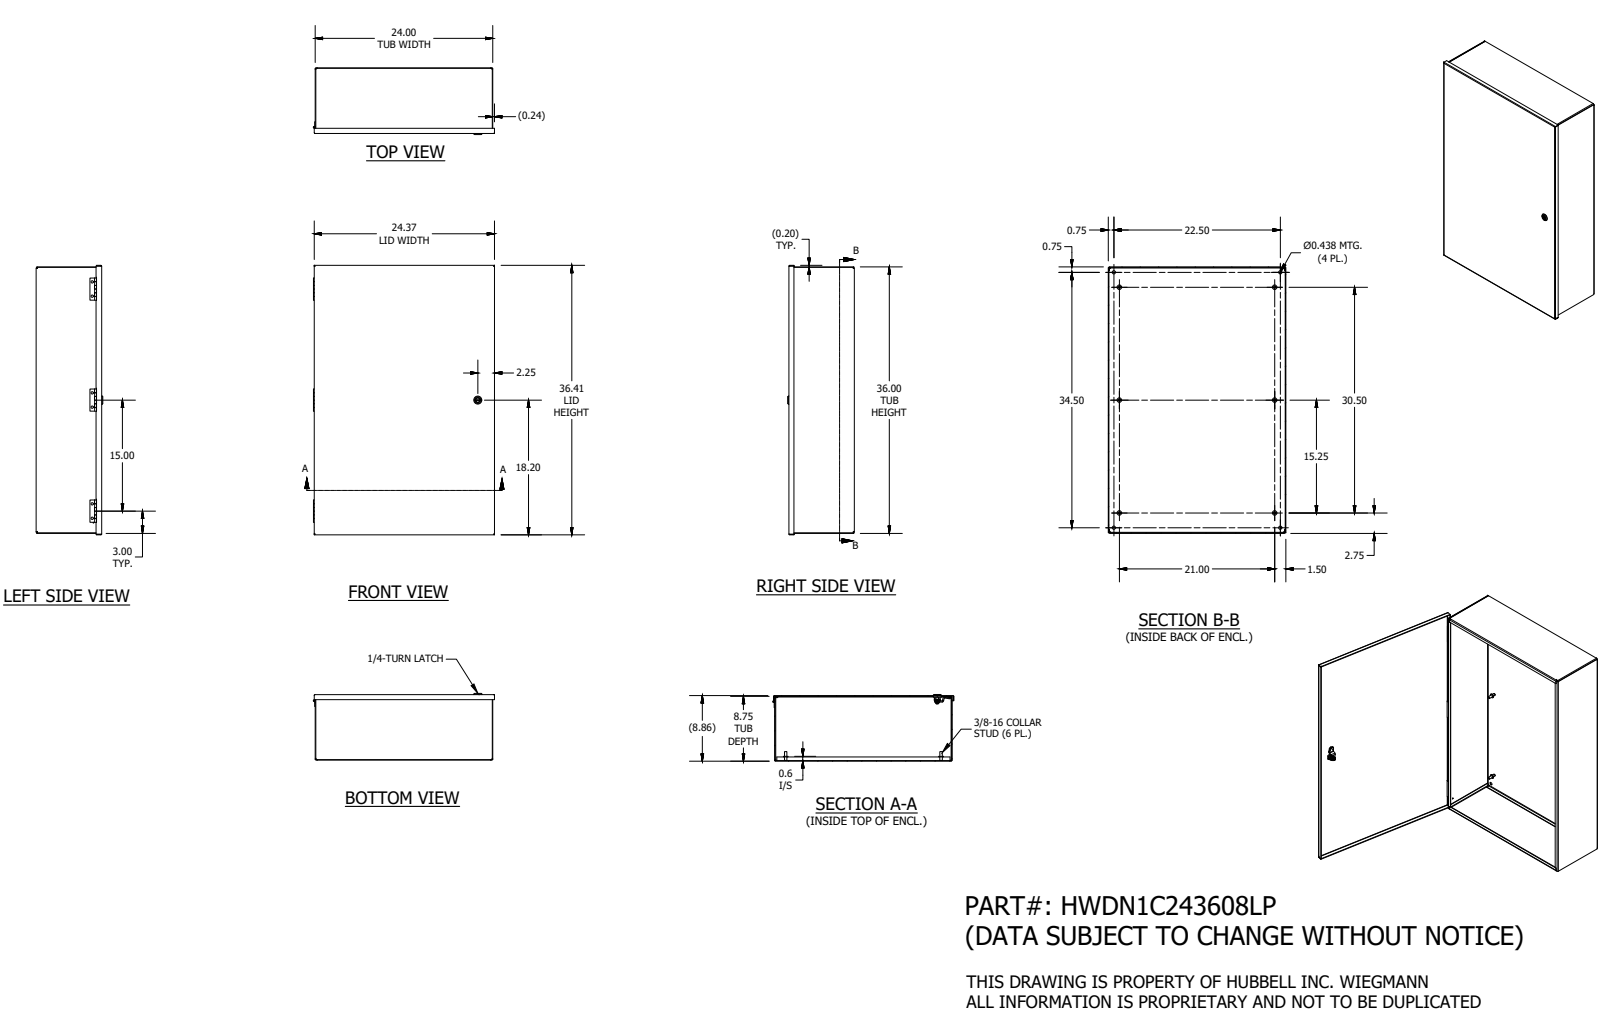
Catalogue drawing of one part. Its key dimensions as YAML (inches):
part_name: "N1C243608LPBLR; N1C2408LPTB; N1C2436LPLID; 1000-101-GPF_GPD (+8 more)"
step_written_by: "Autodesk Inventor 2016 (AUTOMOTIVE_DESIGN)"
units: inches
bodies: {solids: 26, faces: 780, planar: 476, cylindrical: 233, other: 71}
overall_size: [36.406, 24.489, 9.013]
volume: 220.2
surface_area: 5978
round_holes:
  - {diameter: 0.313, count: 6}
  - {diameter: 0.437, count: 4}
  - {diameter: 0.12, count: 1}
  - {diameter: 0.13, count: 1}
  - {diameter: 0.197, count: 1}
  - {diameter: 0.315, count: 1}
  - {diameter: 0.394, count: 1}
  - {diameter: 0.402, count: 1}
  - {diameter: 0.634, count: 1}
  - {diameter: 0.802, count: 1}
round_bosses_or_shafts:
  - {diameter: 0.625, count: 6}
  - {diameter: 0.33, count: 6}
  - {diameter: 1.102, count: 1}
  - {diameter: 1.063, count: 1}
  - {diameter: 0.906, count: 1}
  - {diameter: 0.78, count: 1}
  - {diameter: 0.622, count: 1}
  - {diameter: 0.598, count: 1}
partial_cylinders:
  - {radius: 0.012, count: 30}
  - {radius: 0.063, count: 12}
  - {radius: 0.137, count: 12}
  - {radius: 0.02, count: 10}
  - {radius: 0.031, count: 4}
  - {radius: 0.105, count: 4}
  - {radius: 0.157, count: 4}
  - {radius: 0.016, count: 3}
face_to_face_distances: [0.074, 8.781, 8.707, 8.855, 23.926, 35.926, 23.852, 24, 35.852, 36]
hole_center_spacings: [15, 1.94, 13.06, 16.94, 17.296, 22.5, 27.361, 30]
